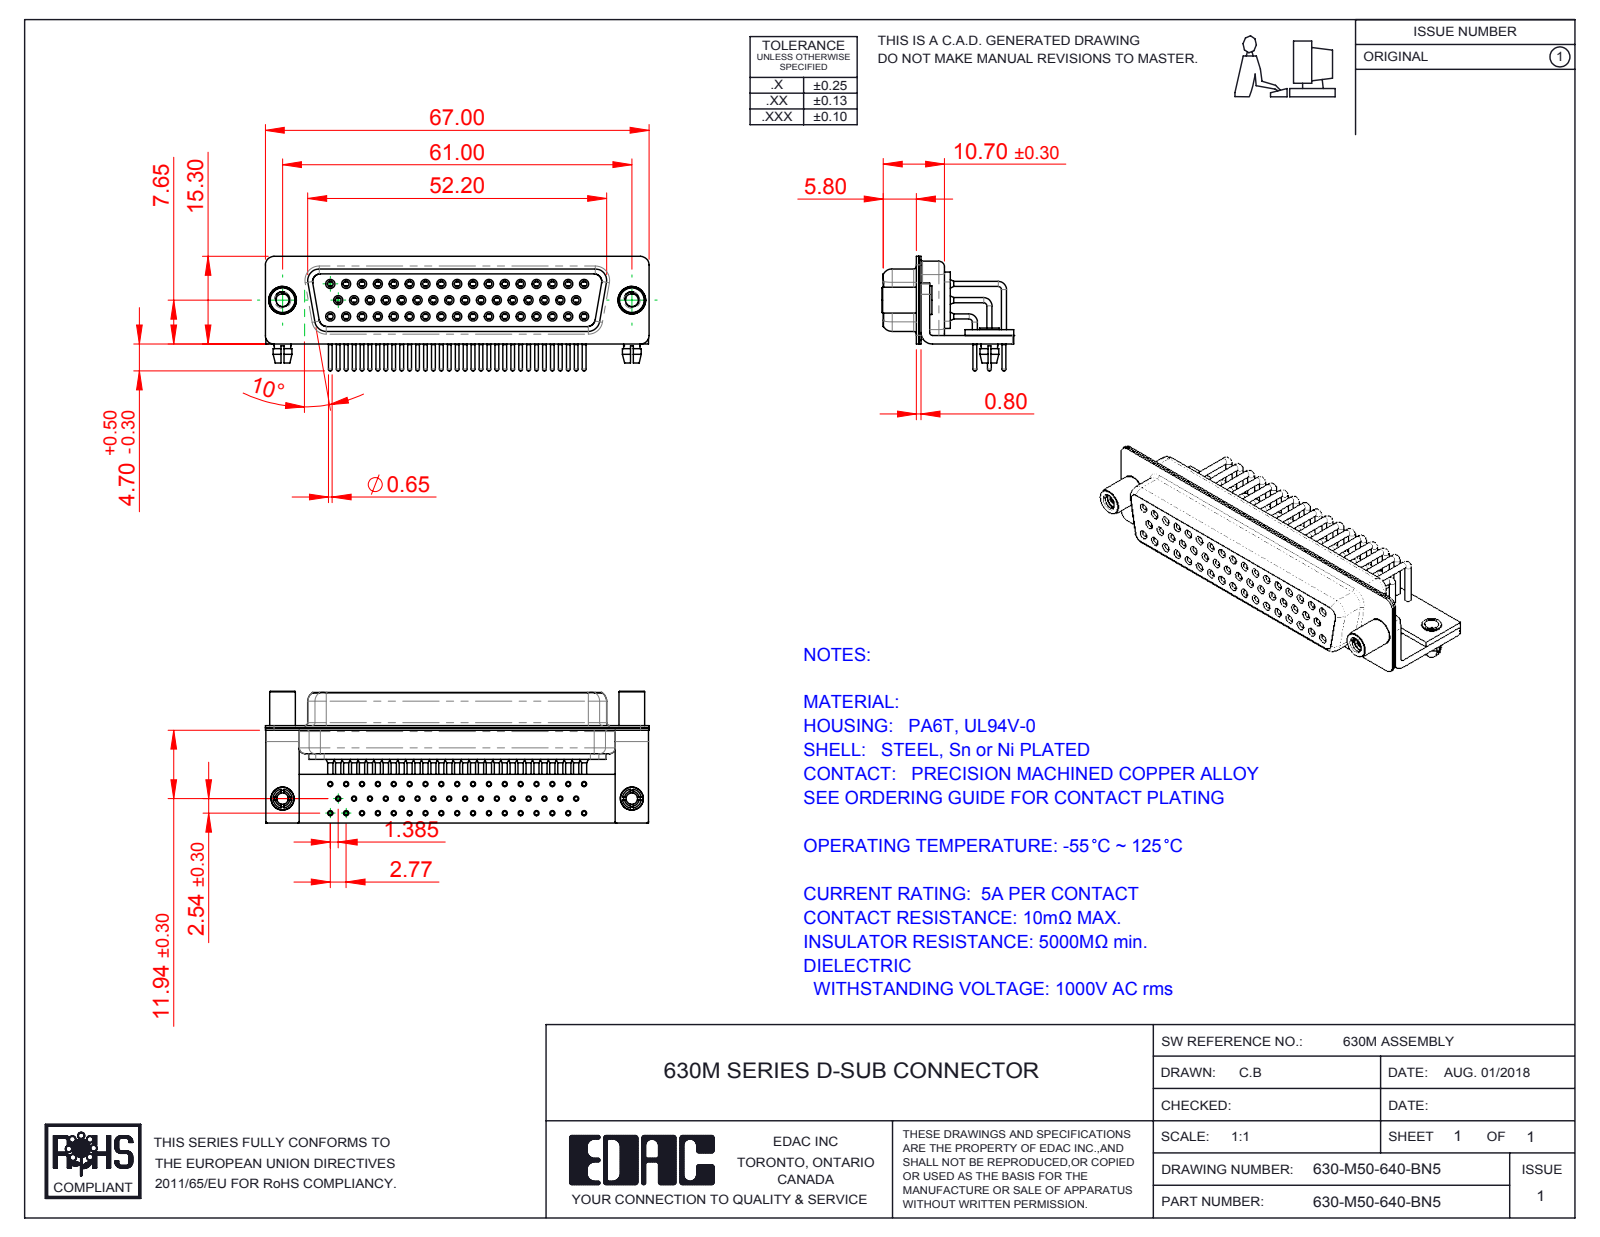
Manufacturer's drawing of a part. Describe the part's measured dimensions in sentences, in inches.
The part is named "630M Board Lock_50 Contacts; 630M Contact Row 3; 630M Stabilizer Board_50 Contacts; 630-M50-640-BN5 (+7 more)". Its 3-D file was written by "SolidWorks 2016 (CONFIG_CONTROL_DESIGN)". It is 60 solids with 3221 faces: 893 planar, 1483 cylindrical and 845 other. Overall it measures 2.638 by 0.906 by 0.787 inches. Its volume is 0.49 cubic inches and its surface area 29.71 square inches. Round holes: 52 of diameter 0.079, 50 of diameter 0.035, 50 of diameter 0.039, 50 of diameter 0.043, 50 of diameter 0.067, 50 of diameter 0.071, 2 of diameter 0.089, 2 of diameter 0.098, 2 of diameter 0.126, 2 of diameter 0.157, 2 of diameter 0.189. Round bosses or shafts: 59 of diameter 0.035, 50 of diameter 0.063, 50 of diameter 0.059, 50 of diameter 0.026, 2 of diameter 0.197, 2 of diameter 0.193, 2 of diameter 0.177, 2 of diameter 0.157. Partial cylindrical surfaces (rounded edges, fillets, slot ends): 16 of radius 0.01, 16 of radius 0.059, 13 of radius 0.079, 8 of radius 0.053, 8 of radius 0.063, 5 of radius 0.02, 4 of radius 0.024, 4 of radius 0.026. The main face-to-face distances are 0.016, 0.039, 0.087, 0.033, 0.053, 0.467, 0.482, 0.228, 0.031, 0.232. The hole center spacings are 0.109, 0.218, 0.327, 0.436, 0.545, 0.654, 0.124, 0.763.
